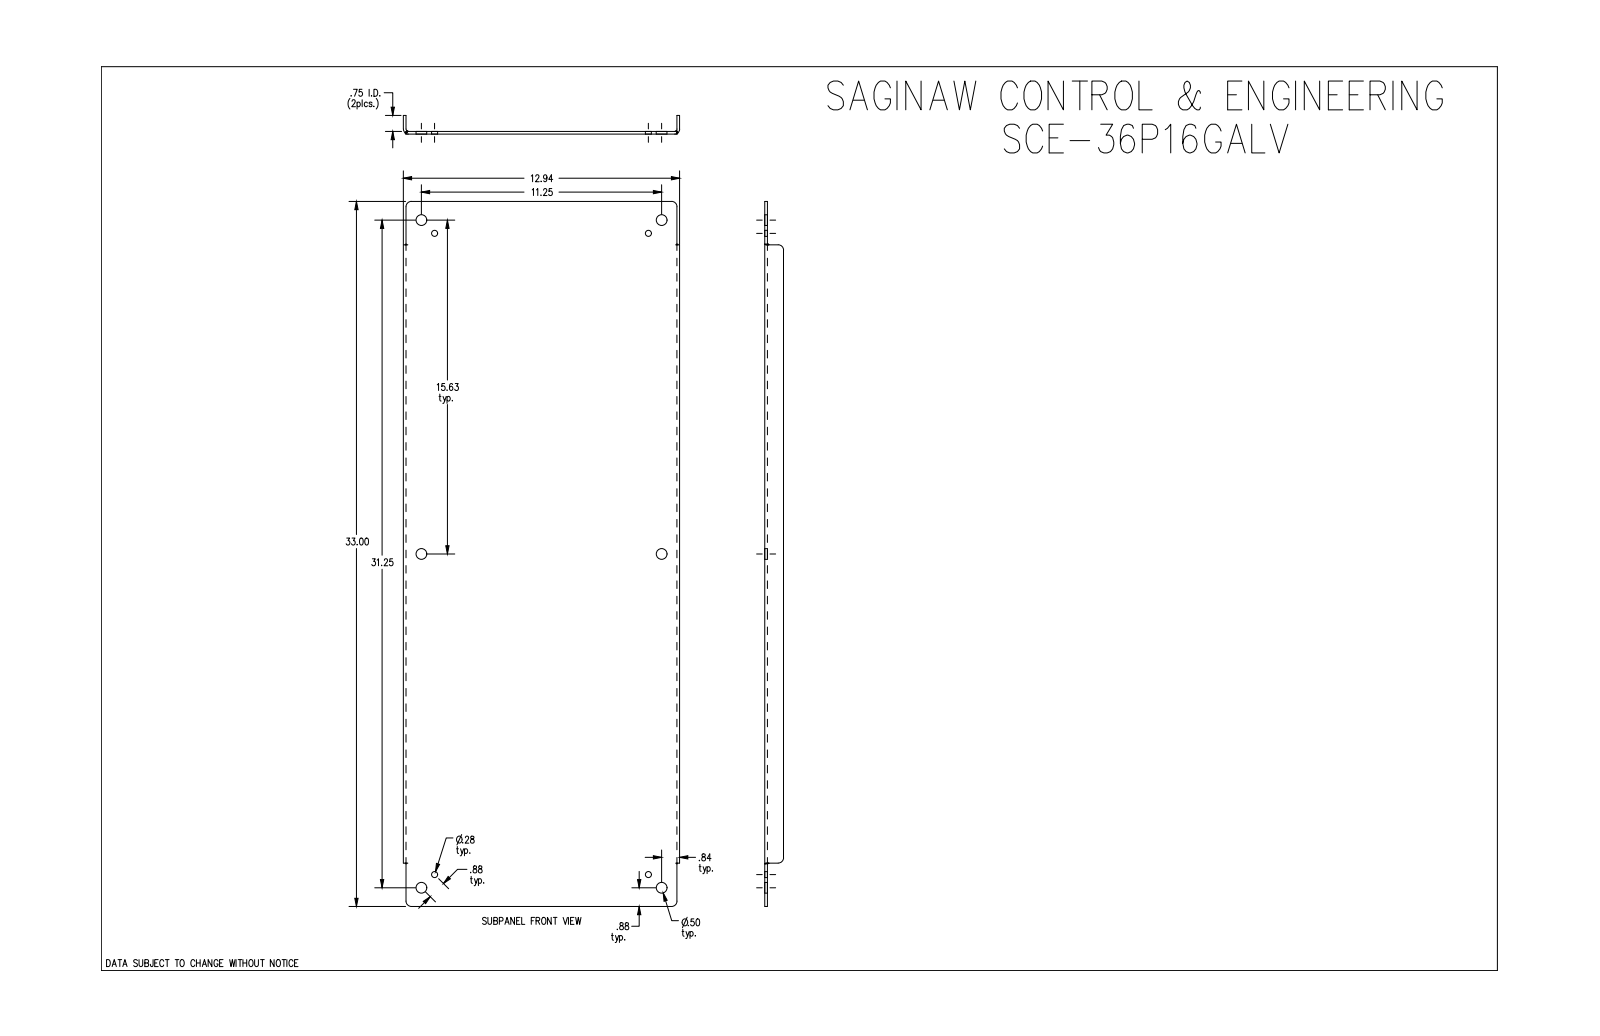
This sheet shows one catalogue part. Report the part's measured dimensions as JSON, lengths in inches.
{"part_name": "SCE-36P16GALV", "step_written_by": "SolidWorks 2019 (CONFIG_CONTROL_DESIGN)", "units": "inches", "bodies": {"solids": 1, "faces": 52, "planar": 18, "cylindrical": 22, "other": 12}, "overall_size": [33, 12.938, 0.875], "volume_in3": 57.93, "surface_area_in2": 940.3, "round_holes": [[0.5, 6], [0.281, 4]], "partial_cylinders_radius": [[0.25, 6], [0.112, 2], [0.237, 2]], "face_to_face_distances": [0.125, 0.125, 12.813, 12.687, 12.938, 0.75, 0.875, 33, 2.031, 30.969], "hole_center_spacings": [0.875, 10.65, 15.019, 15.625, 18.391, 19.254, 30.638, 32.424]}
